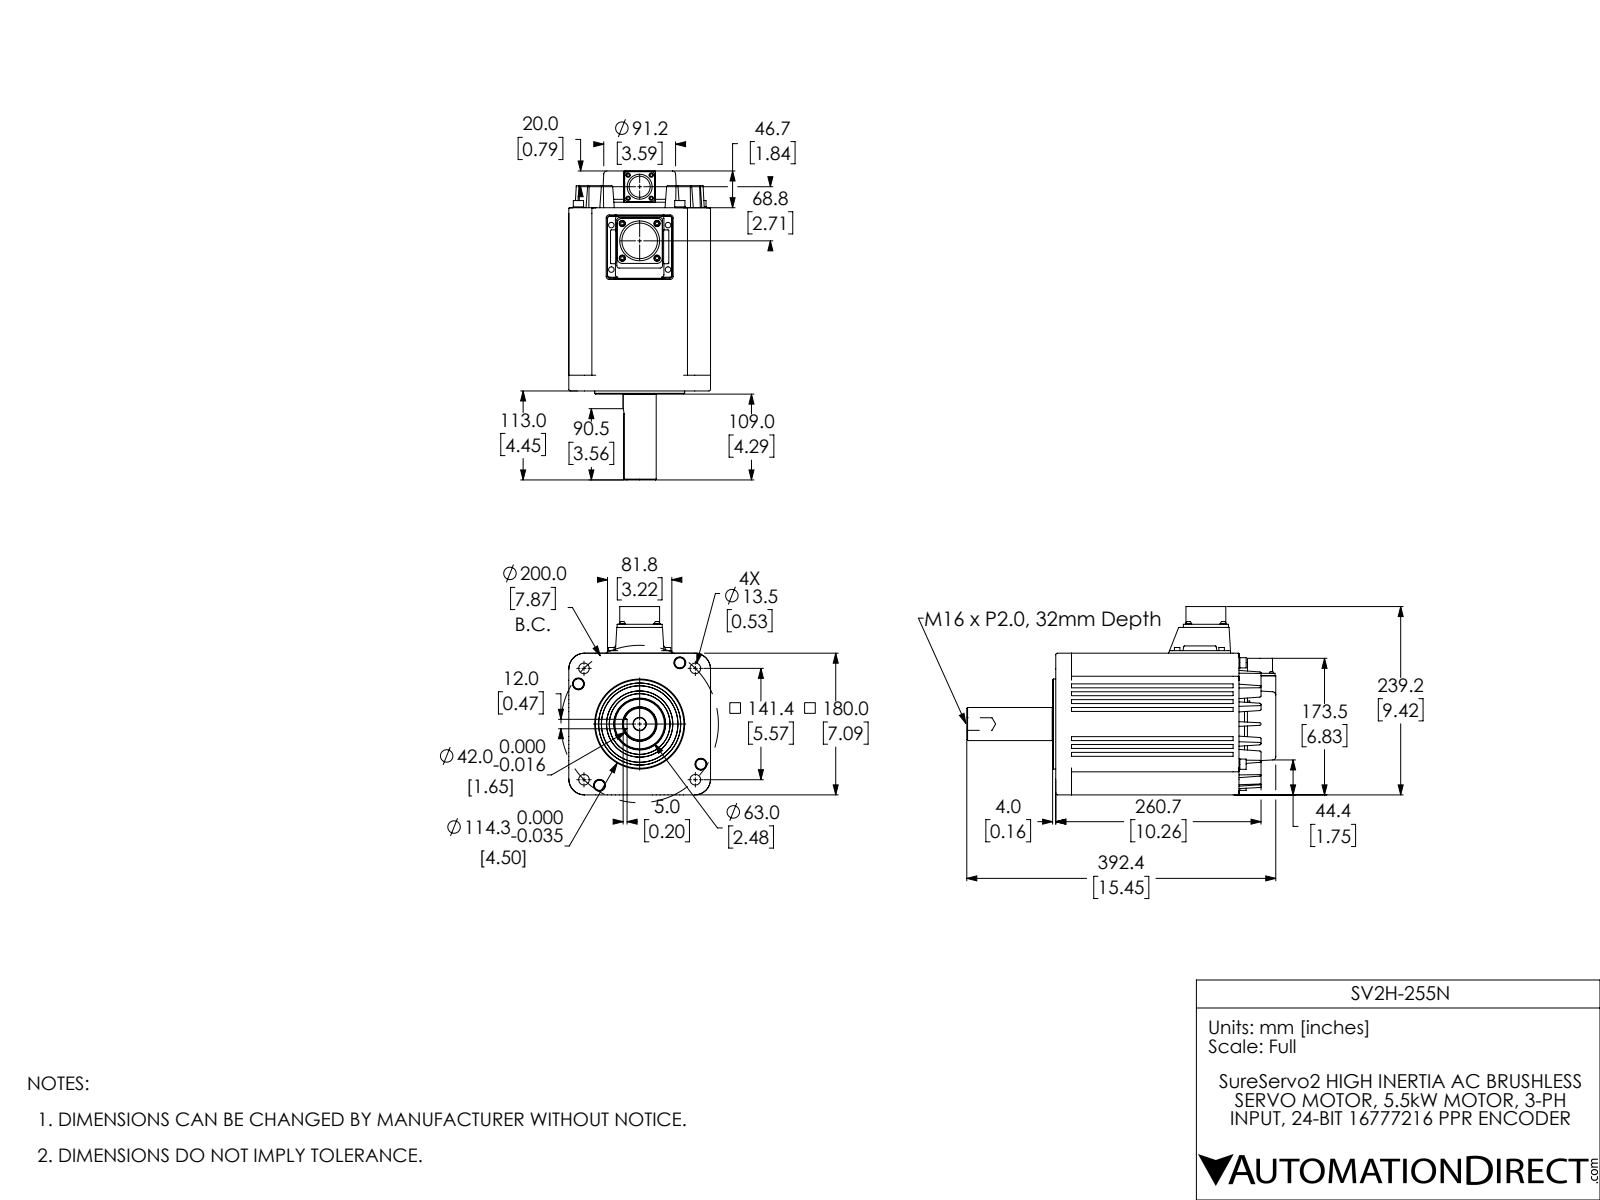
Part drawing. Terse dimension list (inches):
name: SV2H-255N
written by: SolidWorks 2017 (AUTOMOTIVE_DESIGN)
unit: in
bodies: 1 solid, 615 faces (319 planar, 216 cylindrical, 80 other)
size: 15.449 × 9.417 × 7.087
volume: 453.3 in³; area: 573.6 in²
holes: 4× ⌀0.531, 1× ⌀0.63, 1× ⌀1.058, 1× ⌀1.783, 1× ⌀2.48
bosses: 8× ⌀0.315, 4× ⌀0.528, 4× ⌀0.512, 4× ⌀0.276, 3× ⌀0.217, 1× ⌀4.567, 1× ⌀4.5, 1× ⌀1.992
rounds: 16× R0.039, 16× R0.064, 16× R0.197, 8× R0.118, 8× R0.15, 8× R0.157, 4× R0.02, 4× R0.079
face distances: 0.197, 7.087, 0.394, 1.154, 5.933, 0.591, 3.031, 3.228, 2.835, 0.787
hole spacings: 3.937, 5.568, 7.874, 2.707
